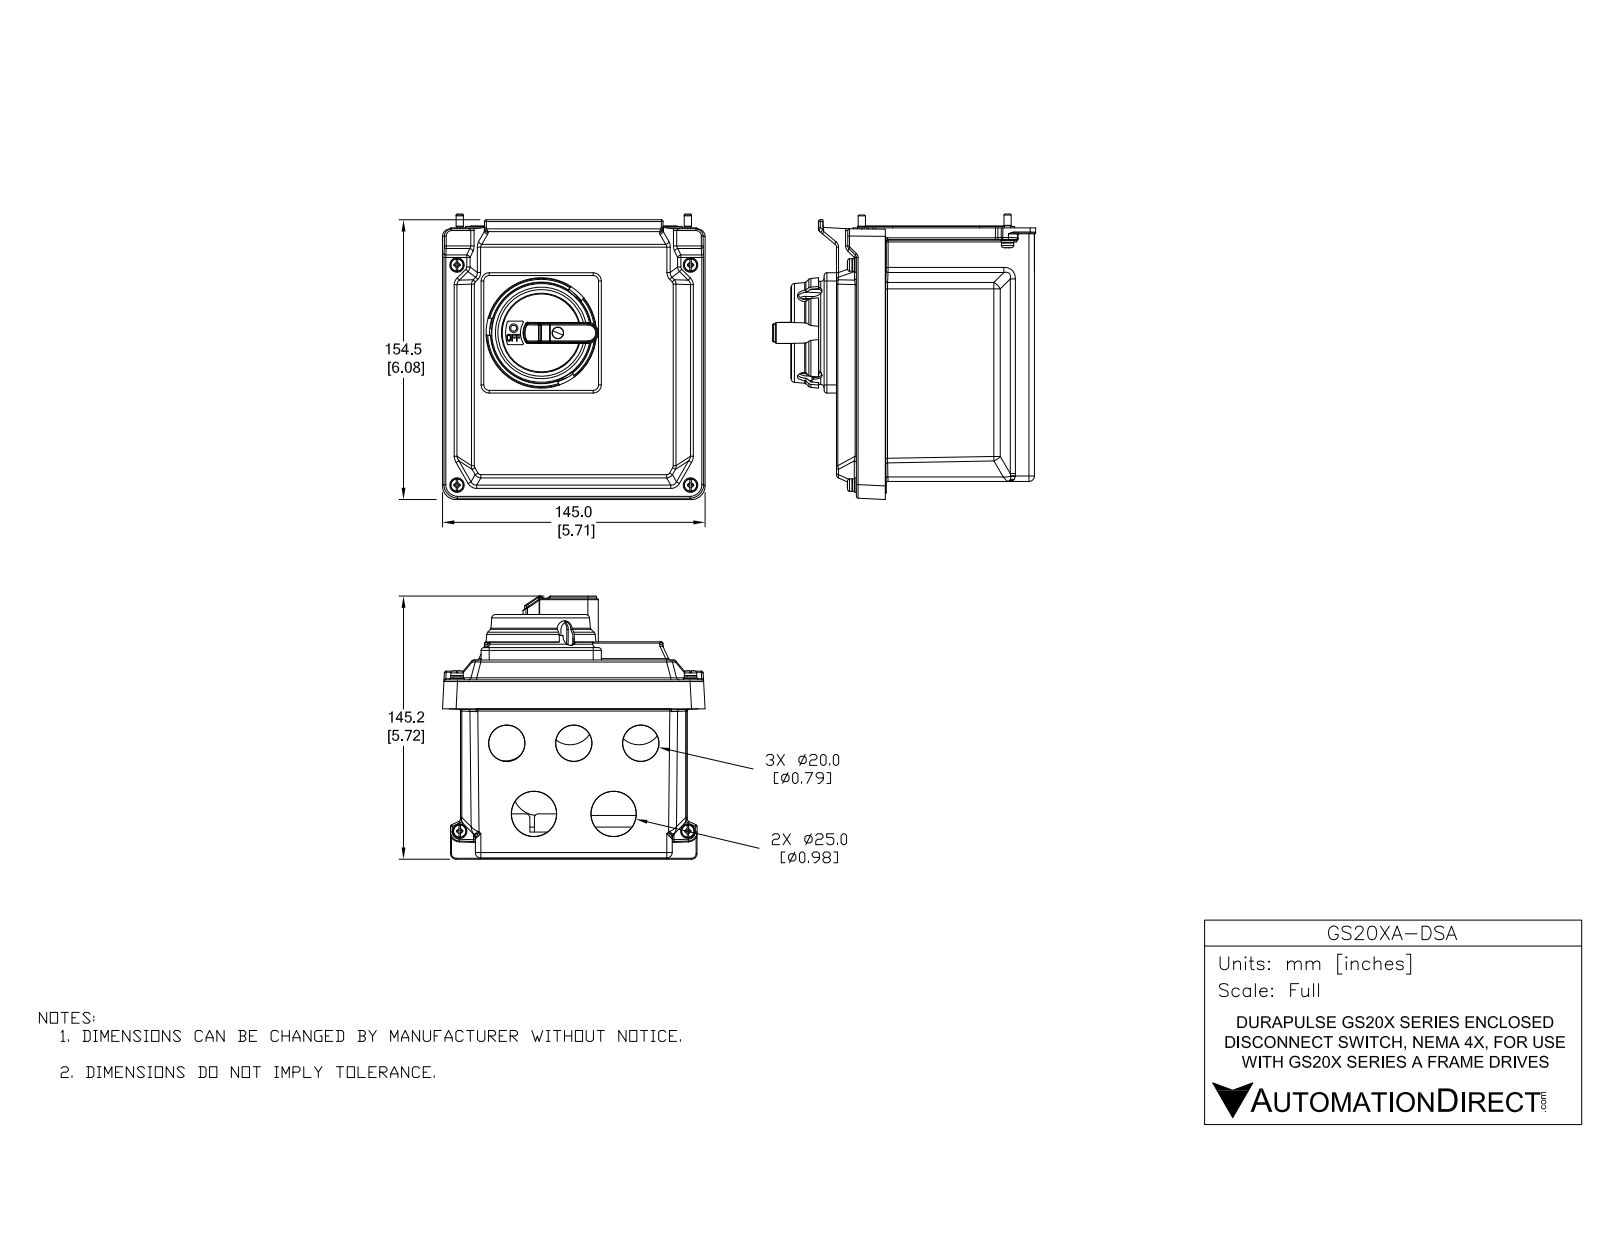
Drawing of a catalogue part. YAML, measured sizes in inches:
part_name: "GS20XA-DSA"
step_written_by: "SolidWorks 2017 (AUTOMOTIVE_DESIGN)"
units: inches
bodies: {solids: 28, faces: 1994, planar: 824, cylindrical: 643, other: 527}
overall_size: [6.205, 5.718, 5.709]
volume: 19.85
surface_area: 382.2
round_holes:
  - {diameter: 0.142, count: 8}
  - {diameter: 0.138, count: 4}
  - {diameter: 0.189, count: 4}
  - {diameter: 0.224, count: 4}
  - {diameter: 0.591, count: 3}
  - {diameter: 0.315, count: 2}
  - {diameter: 0.185, count: 1}
  - {diameter: 0.243, count: 1}
  - {diameter: 0.34, count: 1}
  - {diameter: 0.63, count: 1}
  - {diameter: 0.803, count: 1}
  - {diameter: 1.382, count: 1}
round_bosses_or_shafts:
  - {diameter: 0.276, count: 8}
  - {diameter: 0.268, count: 8}
  - {diameter: 0.157, count: 8}
  - {diameter: 0.134, count: 8}
  - {diameter: 0.315, count: 6}
  - {diameter: 0.988, count: 3}
  - {diameter: 0.929, count: 3}
  - {diameter: 0.78, count: 3}
partial_cylinders:
  - {radius: 0.02, count: 92}
  - {radius: 0.039, count: 60}
  - {radius: 0.079, count: 42}
  - {radius: 0.197, count: 24}
  - {radius: 0.098, count: 16}
  - {radius: 0.157, count: 14}
  - {radius: 0.059, count: 11}
  - {radius: 0.118, count: 10}
face_to_face_distances: [0.098, 4.207, 4.305, 4.108, 0.433, 0.321, 0.531, 3.774, 3.242, 0.965]
hole_center_spacings: [1.336, 1.89, 1.11, 1.457, 1.613, 1.623, 2.167, 2.672]
